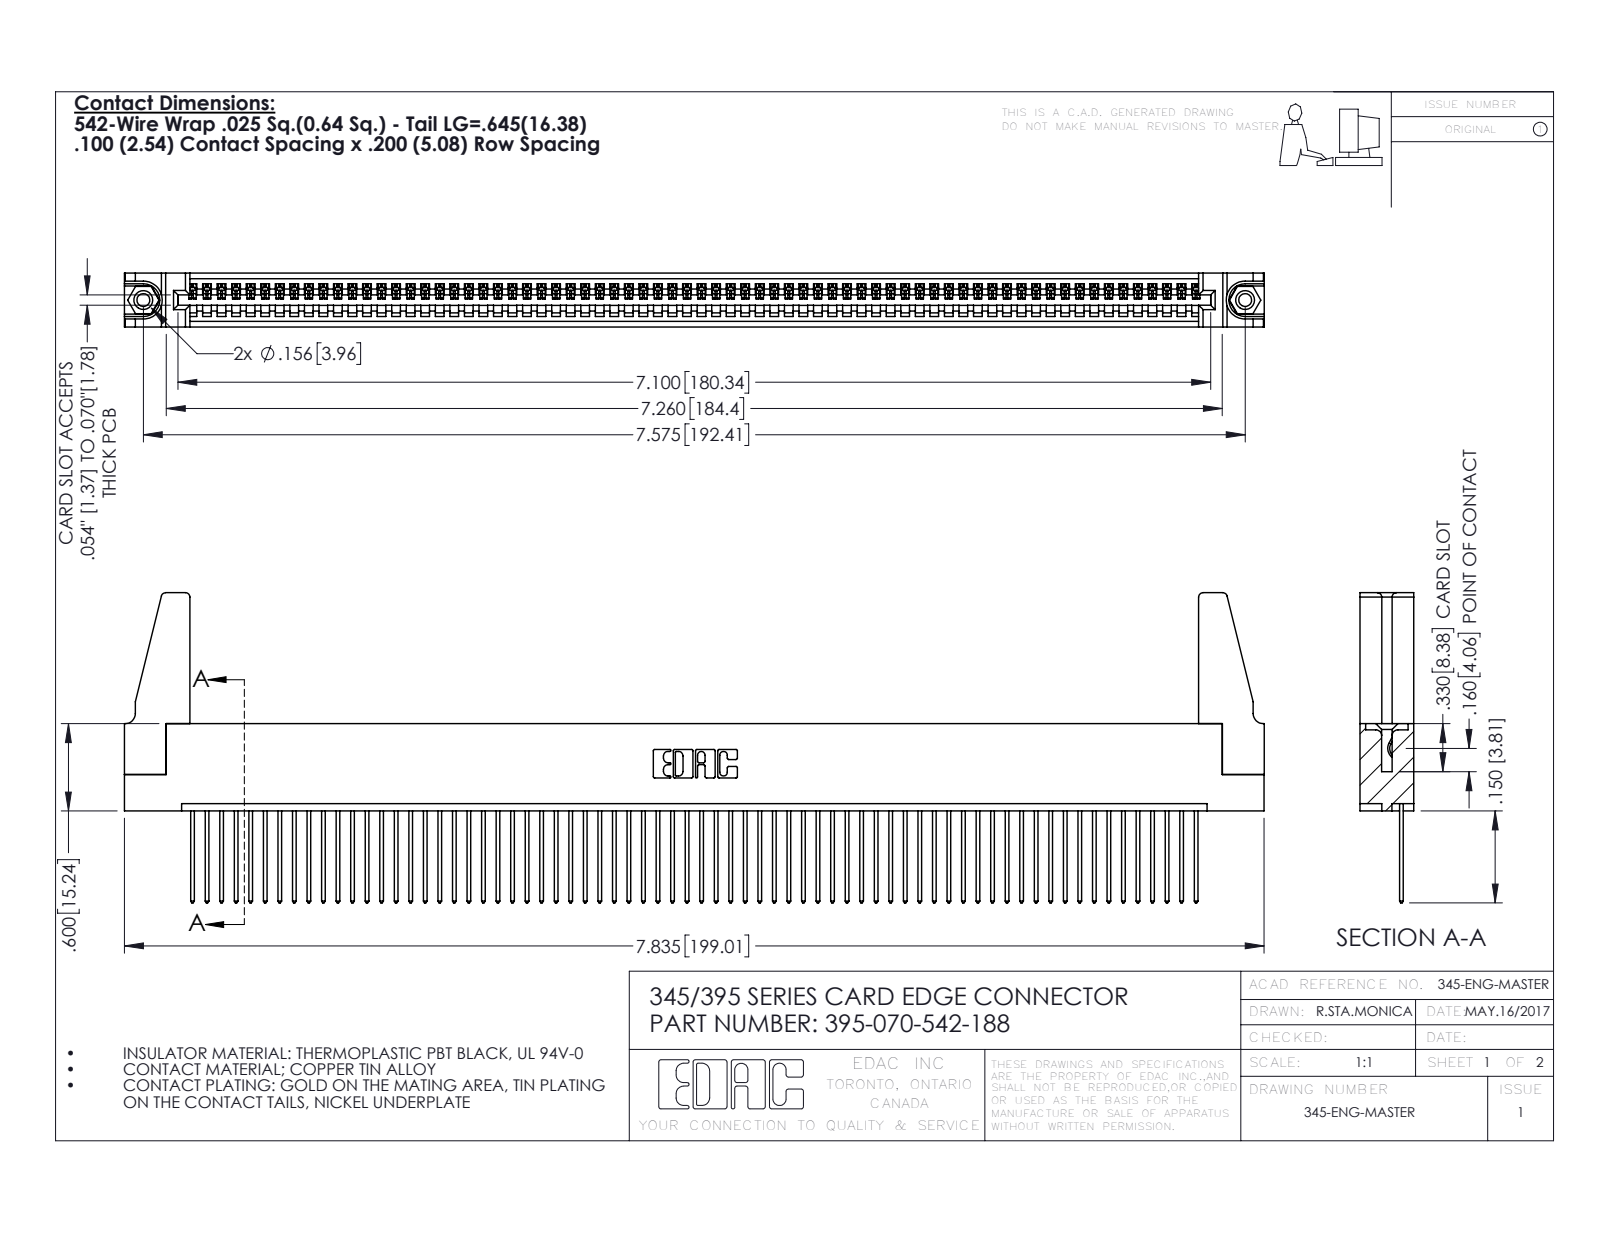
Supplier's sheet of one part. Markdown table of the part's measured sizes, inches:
| quantity | value |
| --- | --- |
| part name | 345 Part_Flush Mounting Lugs - 0.156 Dia-TH; 395-070-542-188; 345-220-078_345-220-088; 345-292-001_345-293-142 (+1 more) |
| STEP written by | SolidWorks 2016 (CONFIG_CONTROL_DESIGN) |
| units | inches |
| bodies | 75 solids, 4310 faces (2952 planar, 1342 cylindrical, 16 other) |
| overall size | 7.836 × 2.132 × 0.37 |
| volume | 1.376 in³ |
| surface area | 46.7 in² |
| round holes (diameter × count) | 0.089 × 2, 0.125 × 2, 0.156 × 2, 0.064 × 1 |
| round bosses / shafts (diameter × count) | 0.155 × 2 |
| partial cylindrical surfaces (radius × count) | 0.006 × 140, 0.01 × 140, 0.01 × 22, 0.03 × 8, 0.007 × 6, 0.031 × 6, 0.026 × 3, 0.031 × 2 |
| main face-to-face distances | 0.072, 0.298, 0.37, 0.098, 0.272, 0.025, 0.2, 0.225, 0.149, 0.072 |
| hole center spacings | 0.27, 7.339, 7.575 |
